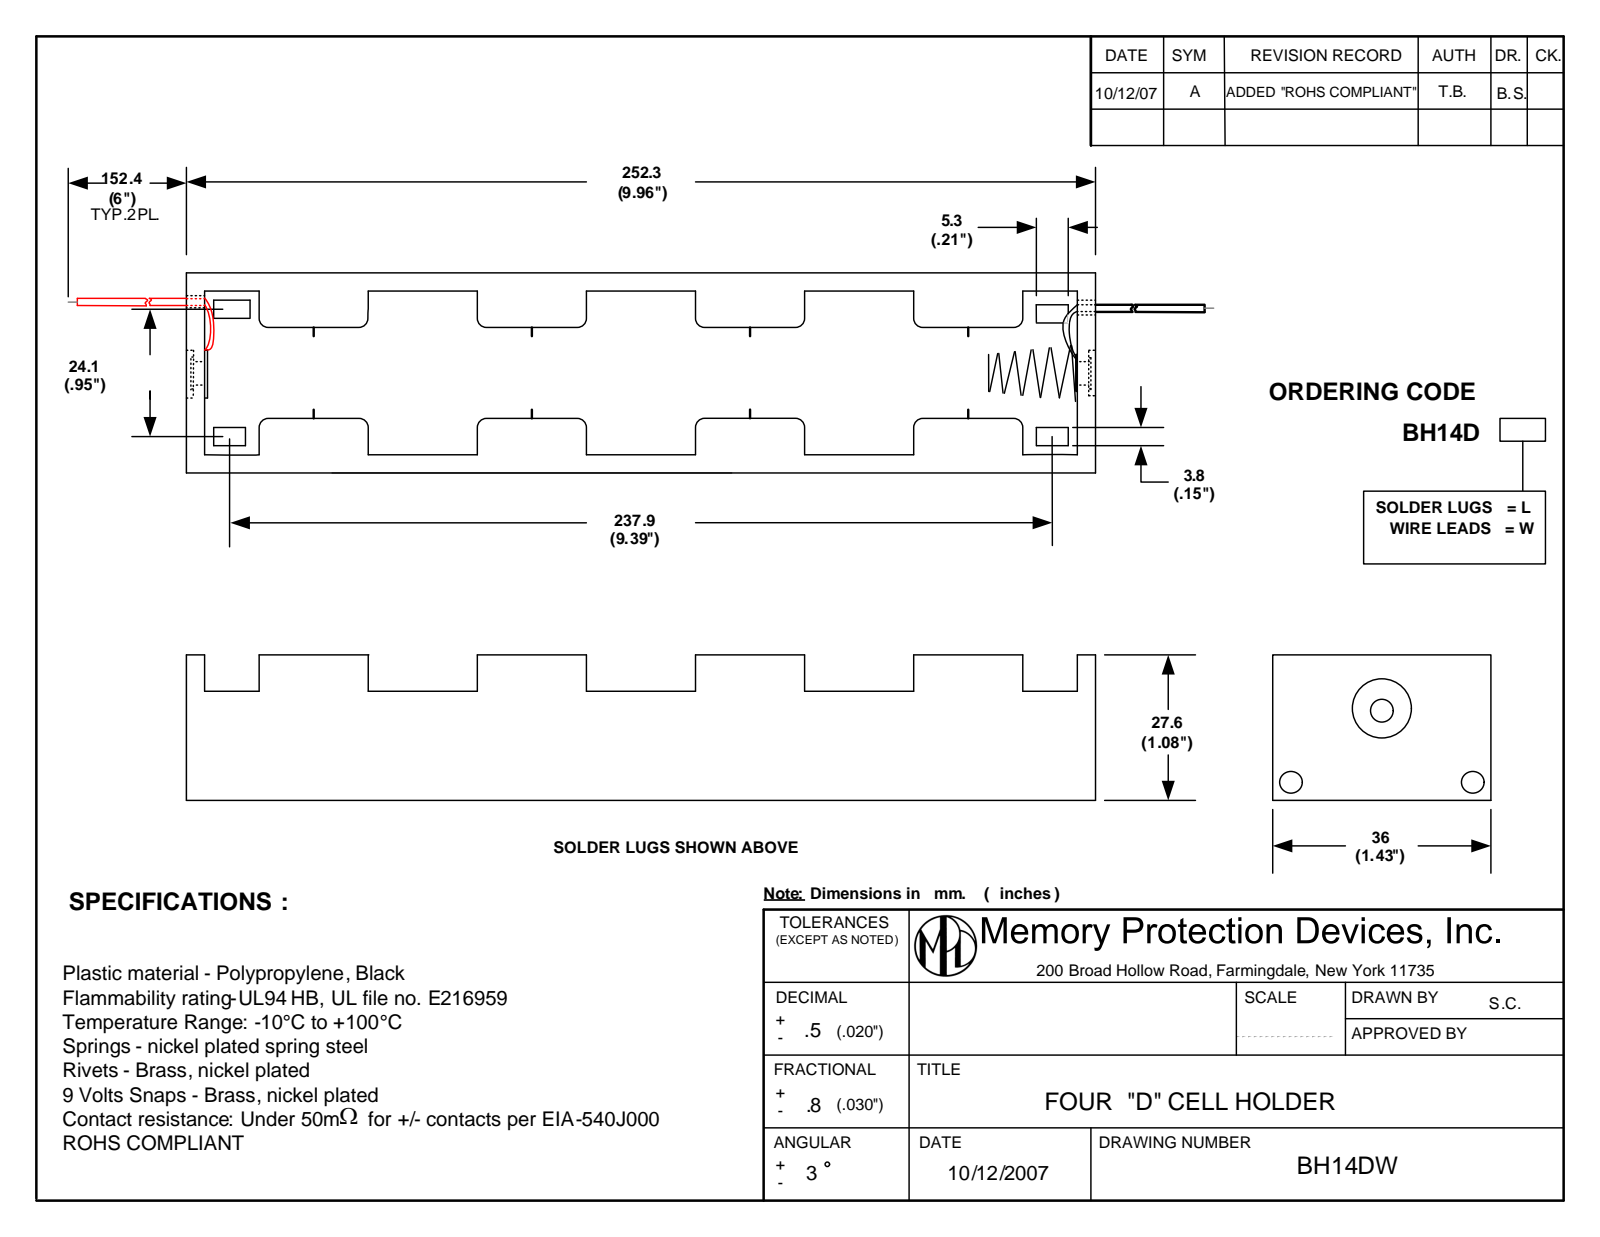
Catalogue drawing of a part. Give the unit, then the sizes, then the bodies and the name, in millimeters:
Units: millimetres
Overall size (bounding box): 557.1 × 36 × 29.02
Round holes (diameter × count): ⌀2.54 ×2, ⌀0.4 ×1, ⌀1.6 ×1, ⌀2.3 ×1, ⌀3 ×1, ⌀8 ×1
Round bosses / shafts (diameter × count): ⌀6.2 ×1, ⌀3.5 ×1, ⌀0.81 ×1, ⌀0.6 ×1
Partial cylindrical surfaces — rounded edges, fillets, slot ends (radius × count): R3 ×16, R4.96 ×2, R5.68 ×2
Main face-to-face distances: 1.6, 34.4, 2, 36, 32.8, 250.7, 252.3, 249.1, 19.8, 17.8
Hole centre spacings: 18.52, 29.6
Volume: 39 515 mm³ · Surface area: 48 592 mm²
Bodies: 7 solids, 233 faces (117 planar, 86 cylindrical, 30 other)
Part name (STEP PRODUCT): BH14DW
STEP written by: SolidWorks 2017 (AUTOMOTIVE_DESIGN)
